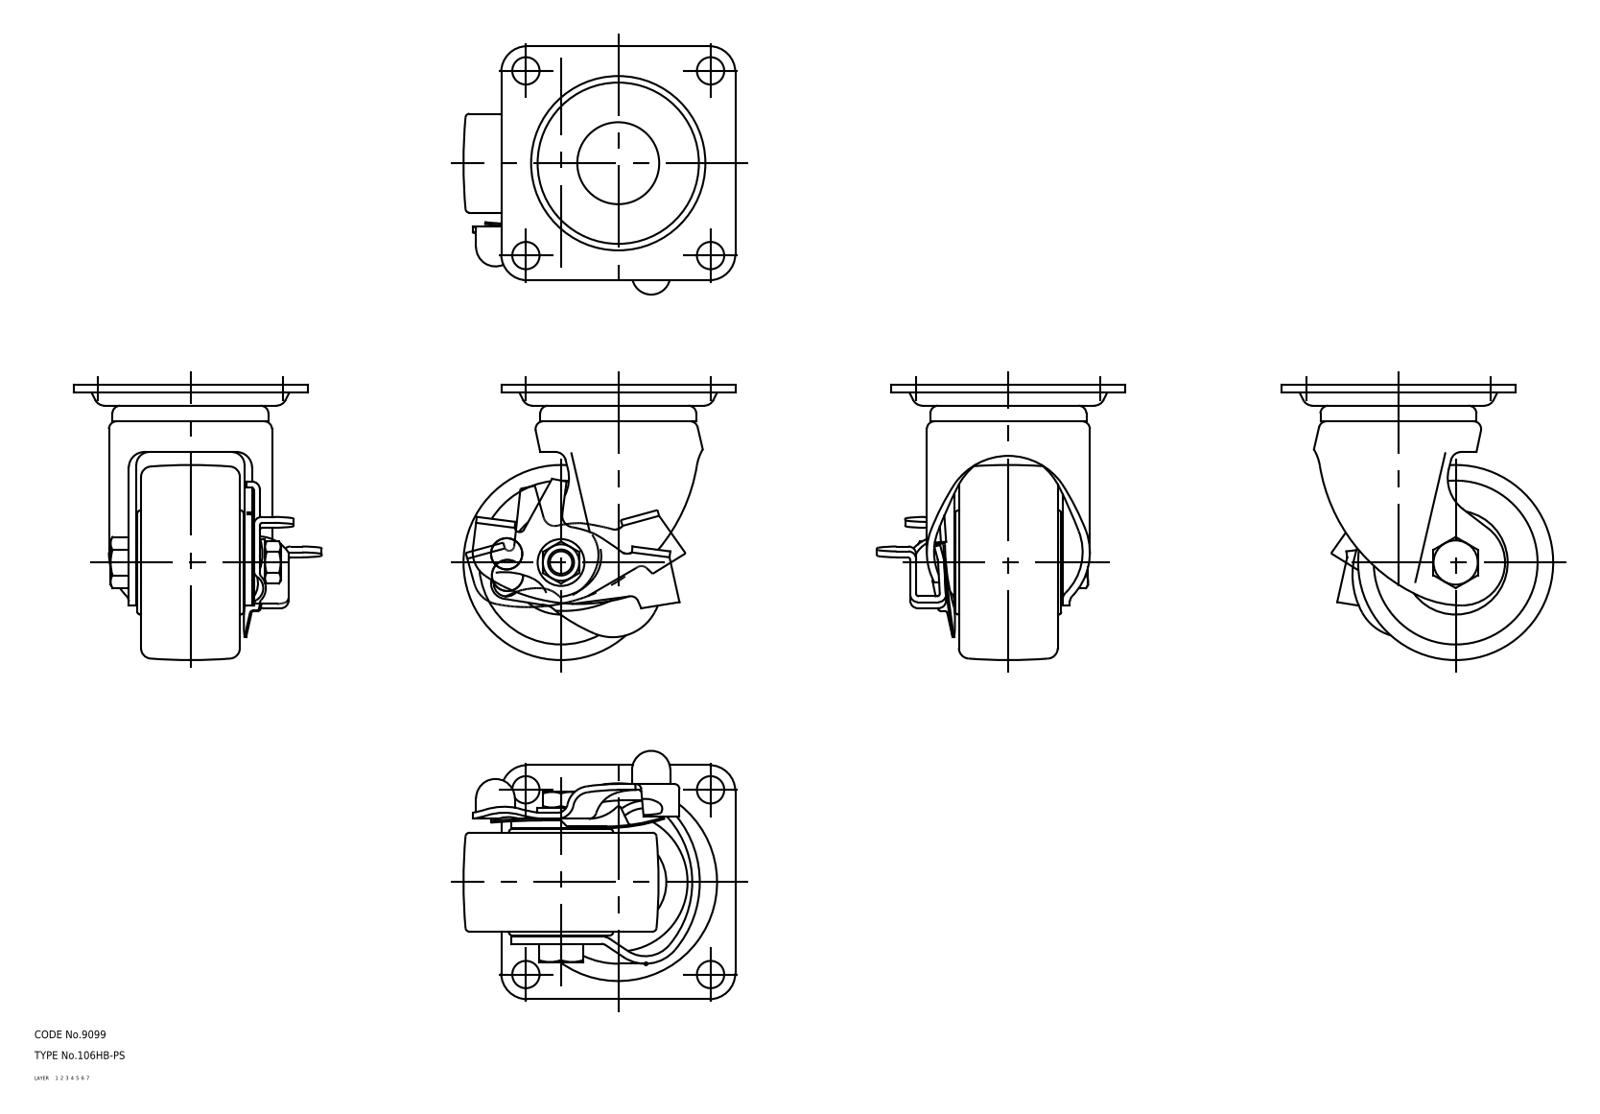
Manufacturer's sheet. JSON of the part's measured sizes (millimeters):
{"part_name": "67134688; 67134701; 67134714; 67134727 (+8 more)", "step_written_by": "CADfix (AUTOMOTIVE_DESIGN)", "units": "millimeters", "bodies": {"solids": 6, "faces": 396, "planar": 0, "cylindrical": 0, "other": 396}, "overall_size": [106, 104.5, 95.5], "volume_mm3": 273339, "surface_area_mm2": 79434}
